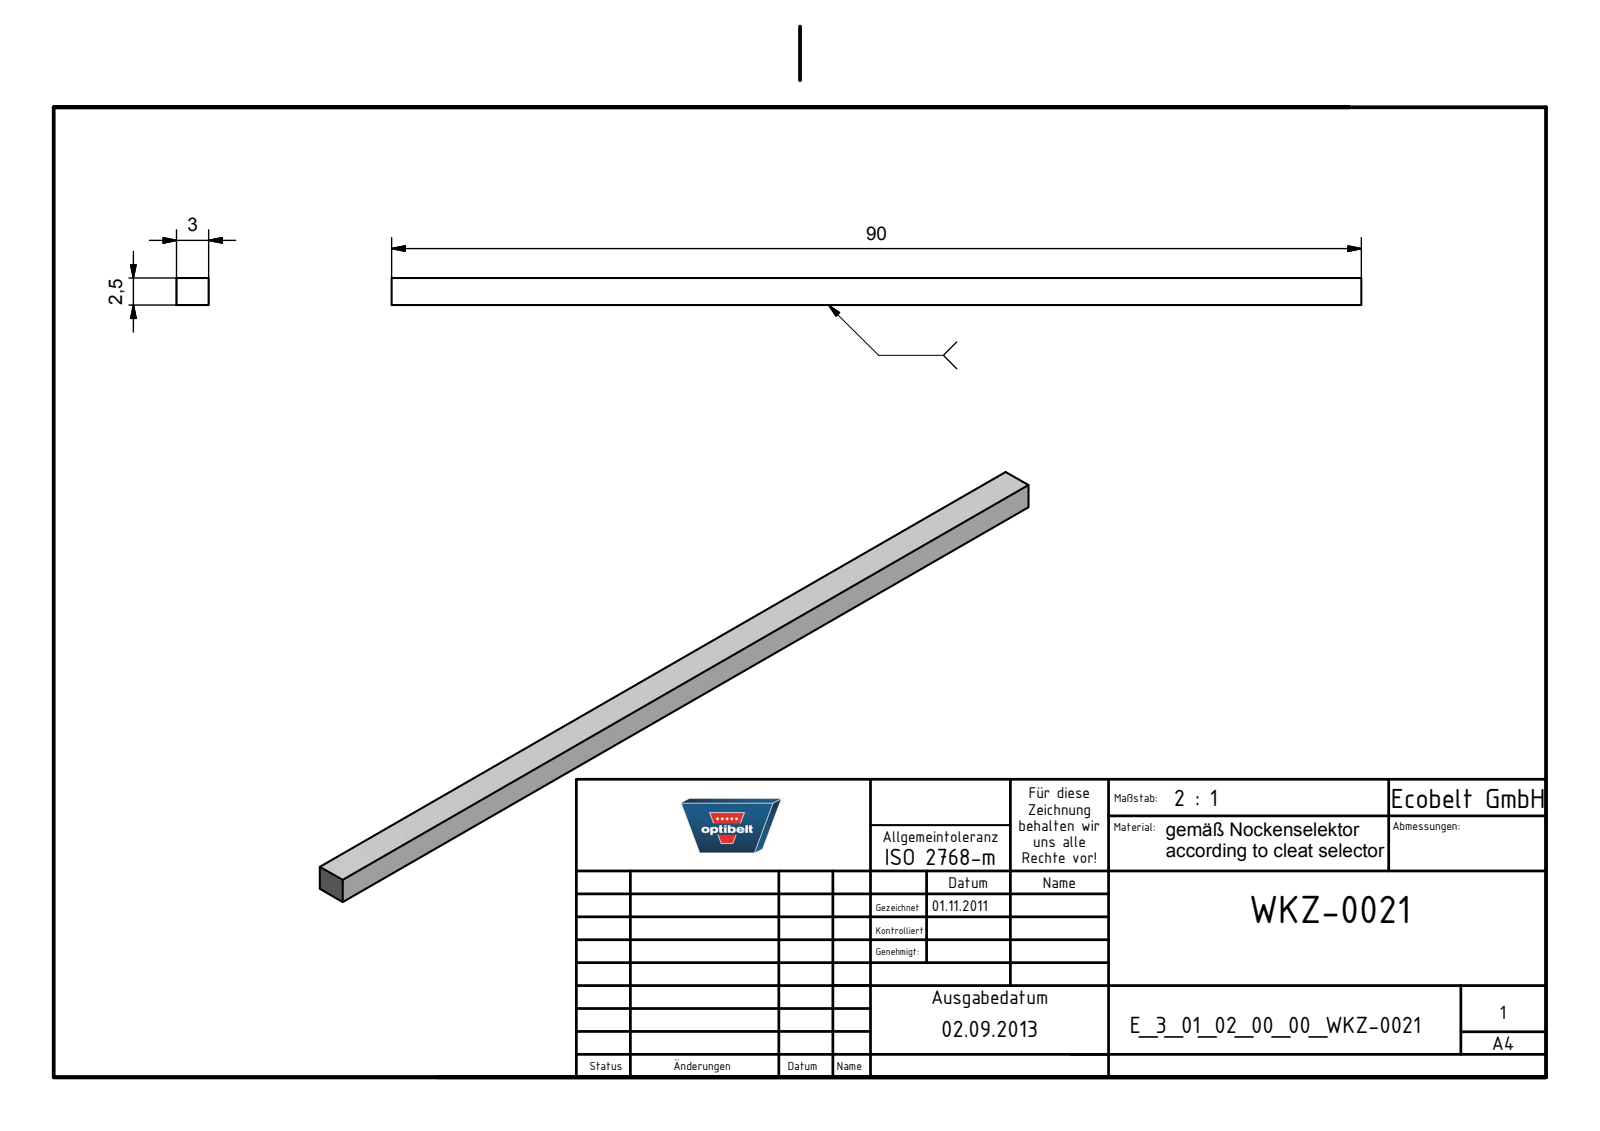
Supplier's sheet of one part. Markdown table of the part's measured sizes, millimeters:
| quantity | value |
| --- | --- |
| part name | E_3_01_02_00_00_WKZ-0021 |
| STEP written by | Autodesk Inventor 2021 (AUTOMOTIVE_DESIGN) |
| units | millimeters |
| bodies | 1 solid, 6 faces (6 planar, 0 cylindrical, 0 other) |
| overall size | 90 × 3 × 2.5 |
| volume | 675 mm³ |
| surface area | 1 005 mm² |
| main face-to-face distances | 2.5, 3, 90 |
